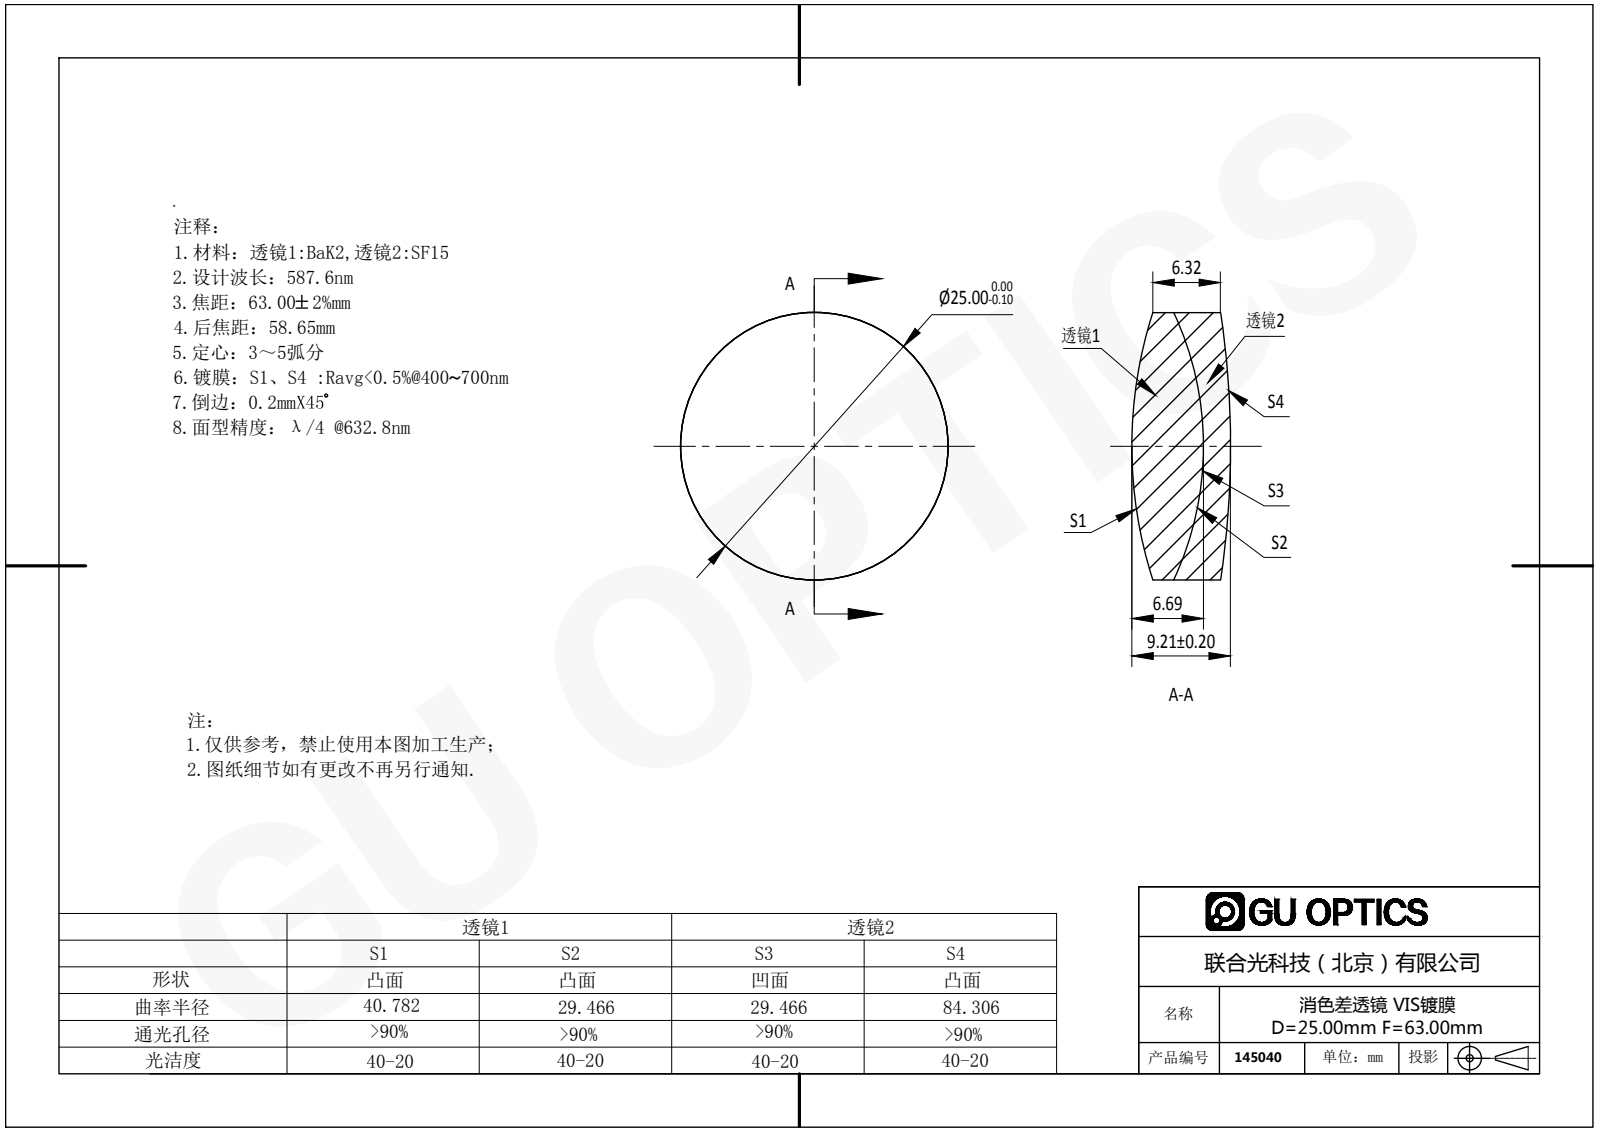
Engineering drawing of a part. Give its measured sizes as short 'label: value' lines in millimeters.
name: 145040
written by: SolidWorks 2016 (AUTOMOTIVE_DESIGN)
unit: mm
bodies: 2 solids, 12 faces (0 planar, 4 cylindrical, 8 other)
size: 25 × 25 × 9.21
volume: 3 815 mm³; area: 2 523 mm²
bosses: 1× ⌀25
